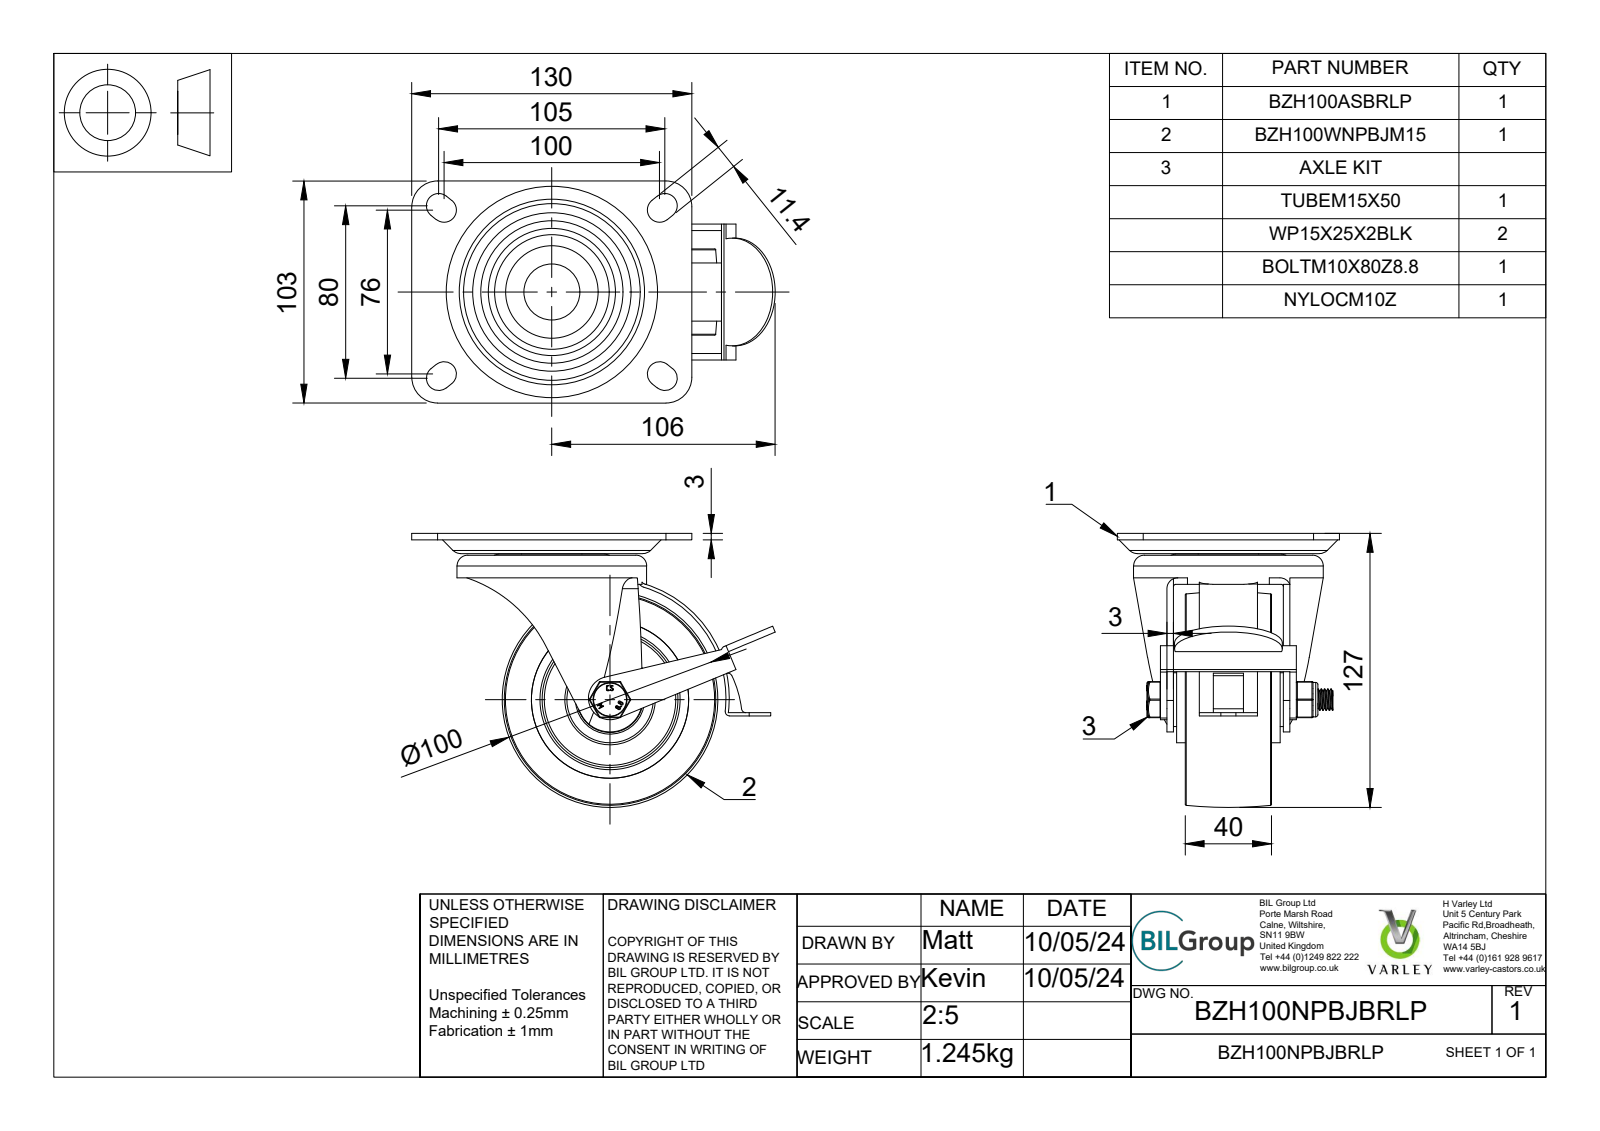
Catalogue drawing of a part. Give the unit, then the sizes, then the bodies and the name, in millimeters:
Units: millimetres
Overall size (bounding box): 168.66 × 127.13 × 103
Round holes (diameter × count): ⌀10 ×1, ⌀10.5 ×1, ⌀12 ×1, ⌀15 ×1, ⌀15.75 ×1, ⌀20.5 ×1, ⌀26.8 ×1, ⌀28 ×1, ⌀28.2 ×1, ⌀30 ×1, ⌀32 ×1, ⌀63 ×1
Round bosses / shafts (diameter × count): ⌀88 ×1, ⌀40 ×1, ⌀36 ×1, ⌀30 ×1, ⌀28 ×1, ⌀26 ×1, ⌀25 ×1, ⌀21.5 ×1
Partial cylindrical surfaces — rounded edges, fillets, slot ends (radius × count): R0.5 ×18, R2 ×8, R5.7 ×8, R0.33 ×4, R0.64 ×4, R12 ×4, R10 ×3, R0.63 ×2
Main face-to-face distances: 3, 40, 8.5, 57, 17.5, 48.5, 26, 31, 22.5, 4
Volume: 354 923 mm³ · Surface area: 165 183 mm²
Bodies: 41 solids, 1165 faces (400 planar, 224 cylindrical, 541 other)
Part name (STEP PRODUCT): BZH100NPBJBRLP v3; BZH100ASBRLP v1; ZINC PLATED, PRESSED STEEL TOP PLATE; ZINC PLATED, PRESSED STEEL FORKS (+8 more)
STEP written by: Autodesk Translation Framework v12.20.1.177 (AUTOMOTIVE_DESIGN)
